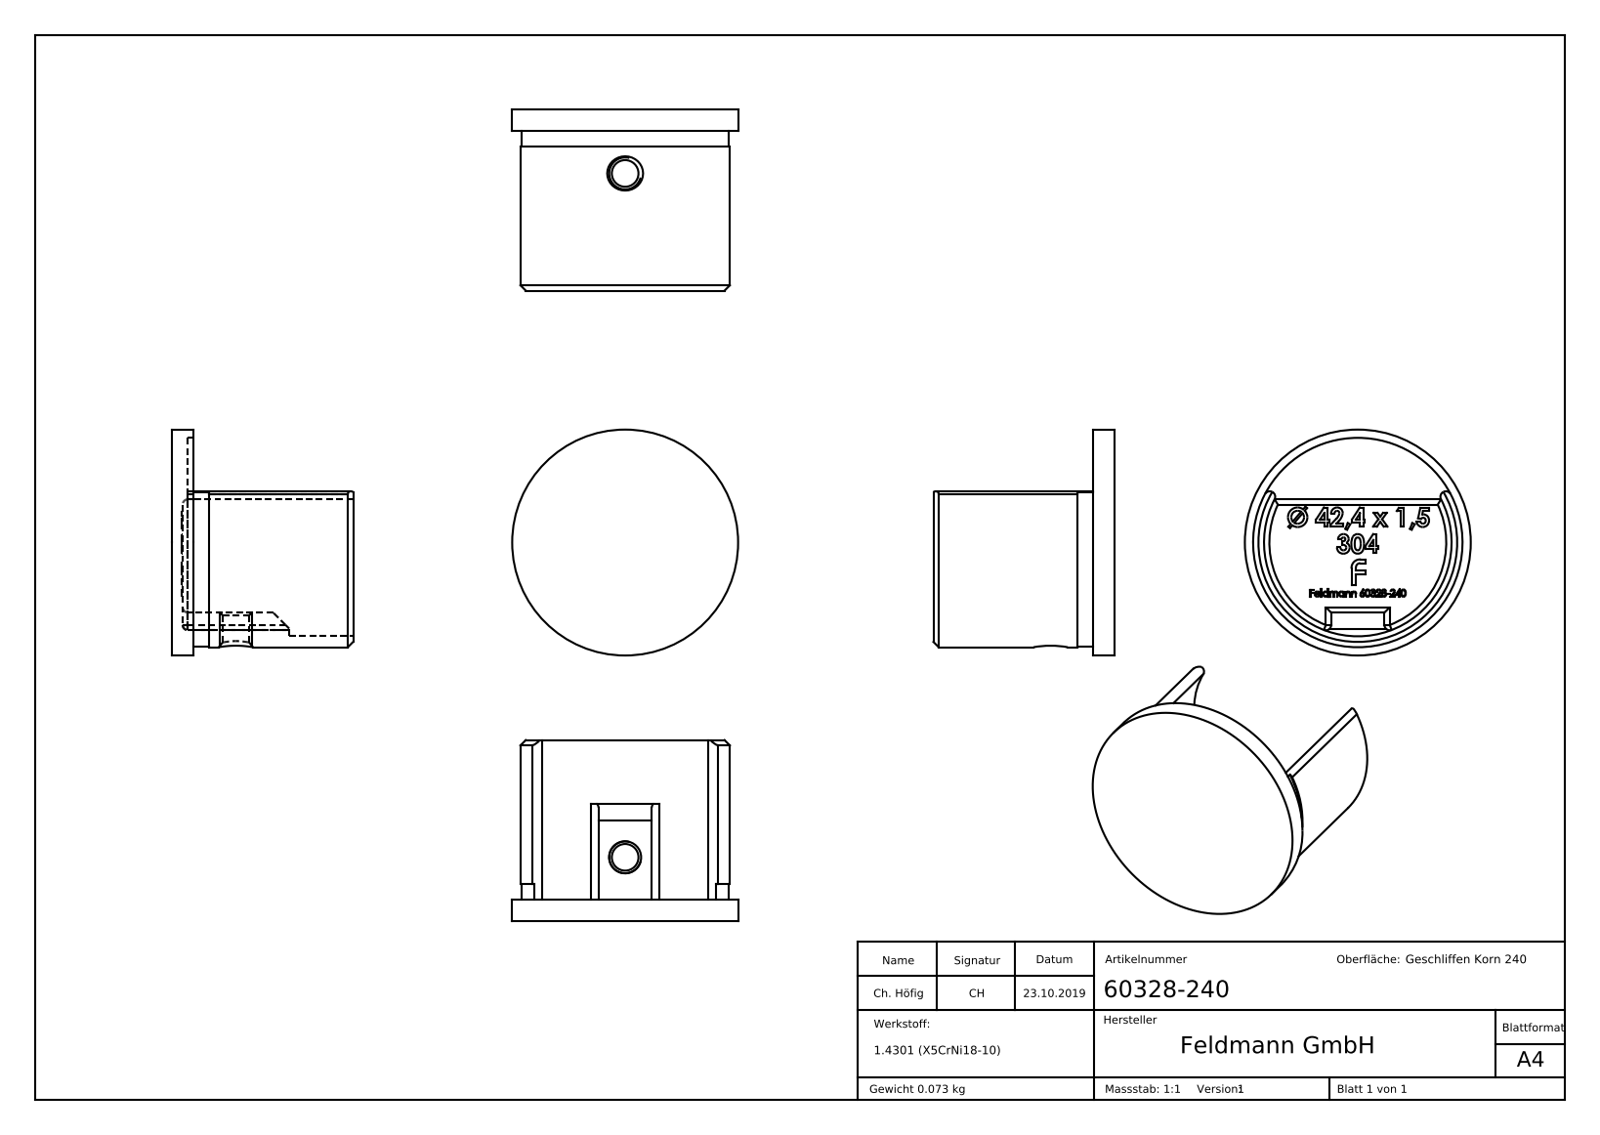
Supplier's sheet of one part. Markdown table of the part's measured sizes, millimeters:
| quantity | value |
| --- | --- |
| part name | 60328-240 |
| STEP written by | SolidWorks 2015 (CONFIG_CONTROL_DESIGN) |
| units | millimeters |
| bodies | 1 solid, 440 faces (250 planar, 14 cylindrical, 176 other) |
| overall size | 42.4 × 42.4 × 34 |
| volume | 9 328 mm³ |
| surface area | 8 466 mm² |
| round holes (diameter × count) | 5 × 1, 39.3 × 1 |
| round bosses / shafts (diameter × count) | 42.4 × 1 |
| partial cylindrical surfaces (radius × count) | 1 × 6, 1.02 × 2, 17.6 × 1, 19.45 × 1 |
| main face-to-face distances | 2, 1, 3, 4, 30, 31, 32, 34, 1.9, 2.1 |
